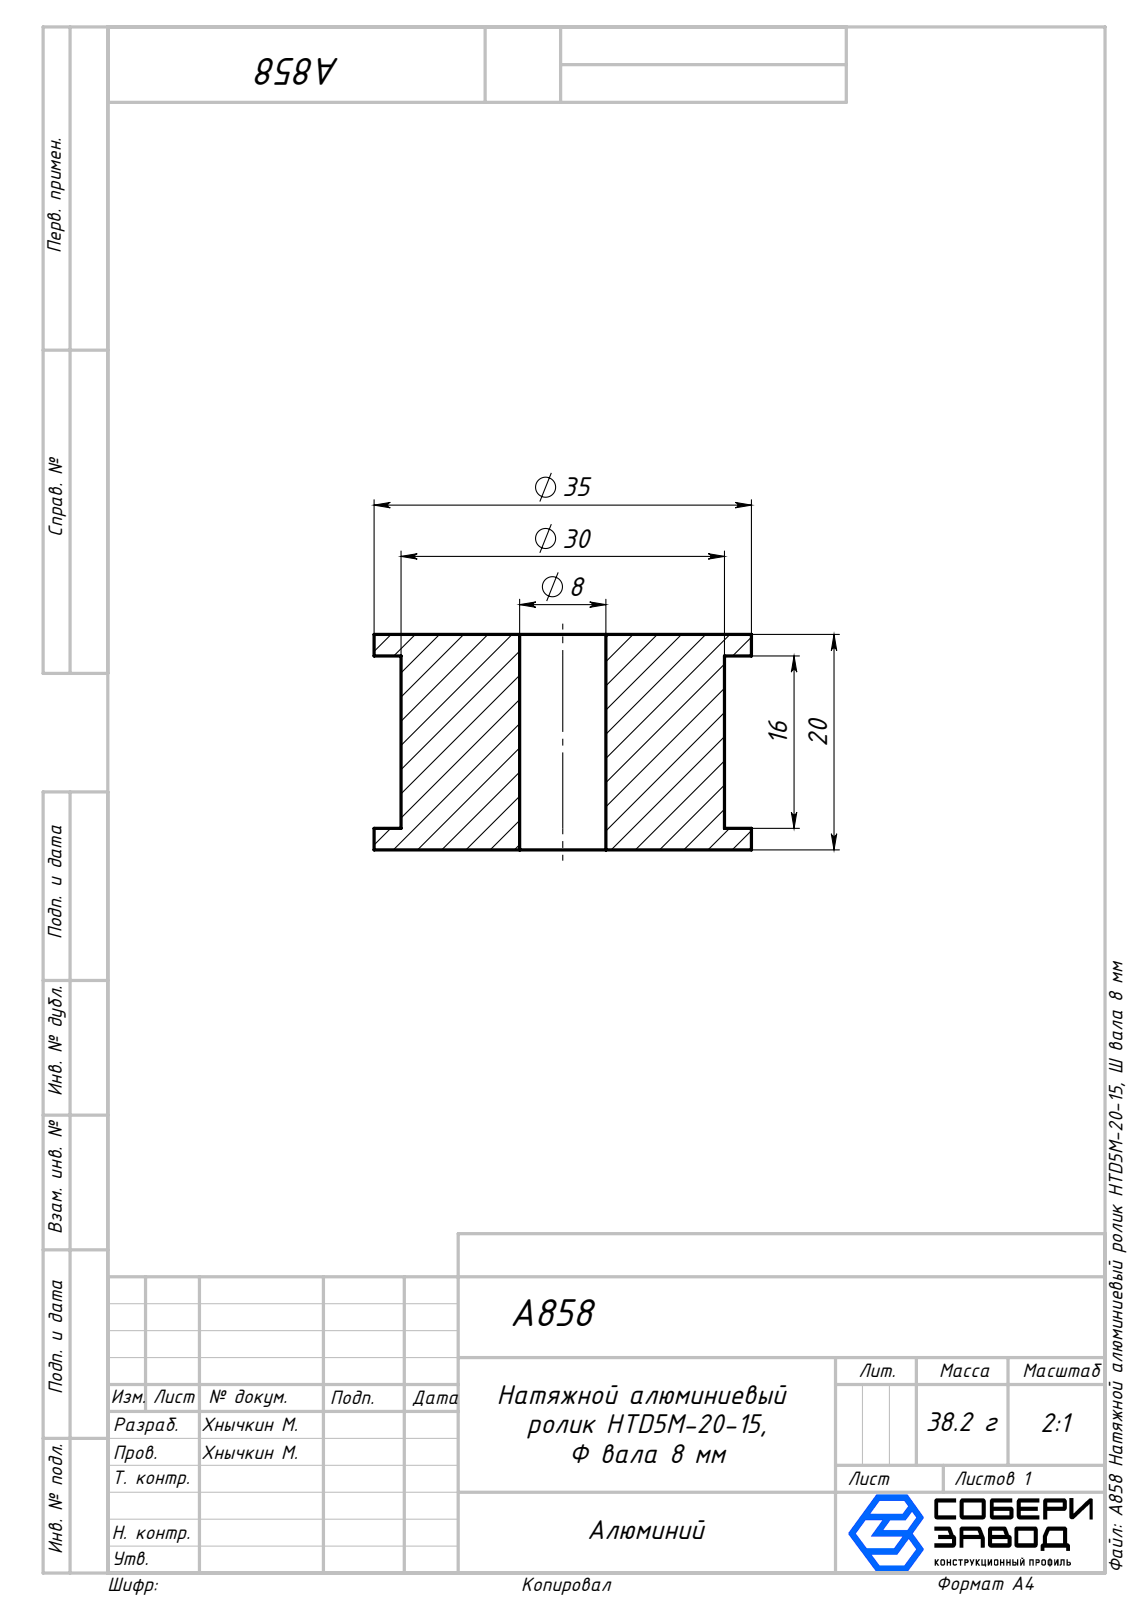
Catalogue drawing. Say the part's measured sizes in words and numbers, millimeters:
The part is named "A858 Натяжной алюминиевый ролик HTD5M-20-15, Ø вала 8 мм". Its 3-D file was written by "SolidWorks 2025 (AUTOMOTIVE_DESIGN)". It is 1 solid with 12 faces: 4 planar, 8 cylindrical and 0 other. Overall it measures 35 by 35 by 20 millimeters. Its volume is 14 153 cubic millimeters and its surface area 4 785 square millimeters. Round holes: 1 of diameter 8. Round bosses or shafts: 1 of diameter 35, 1 of diameter 30. The main face-to-face distances are 20, 2, 18, 16.
